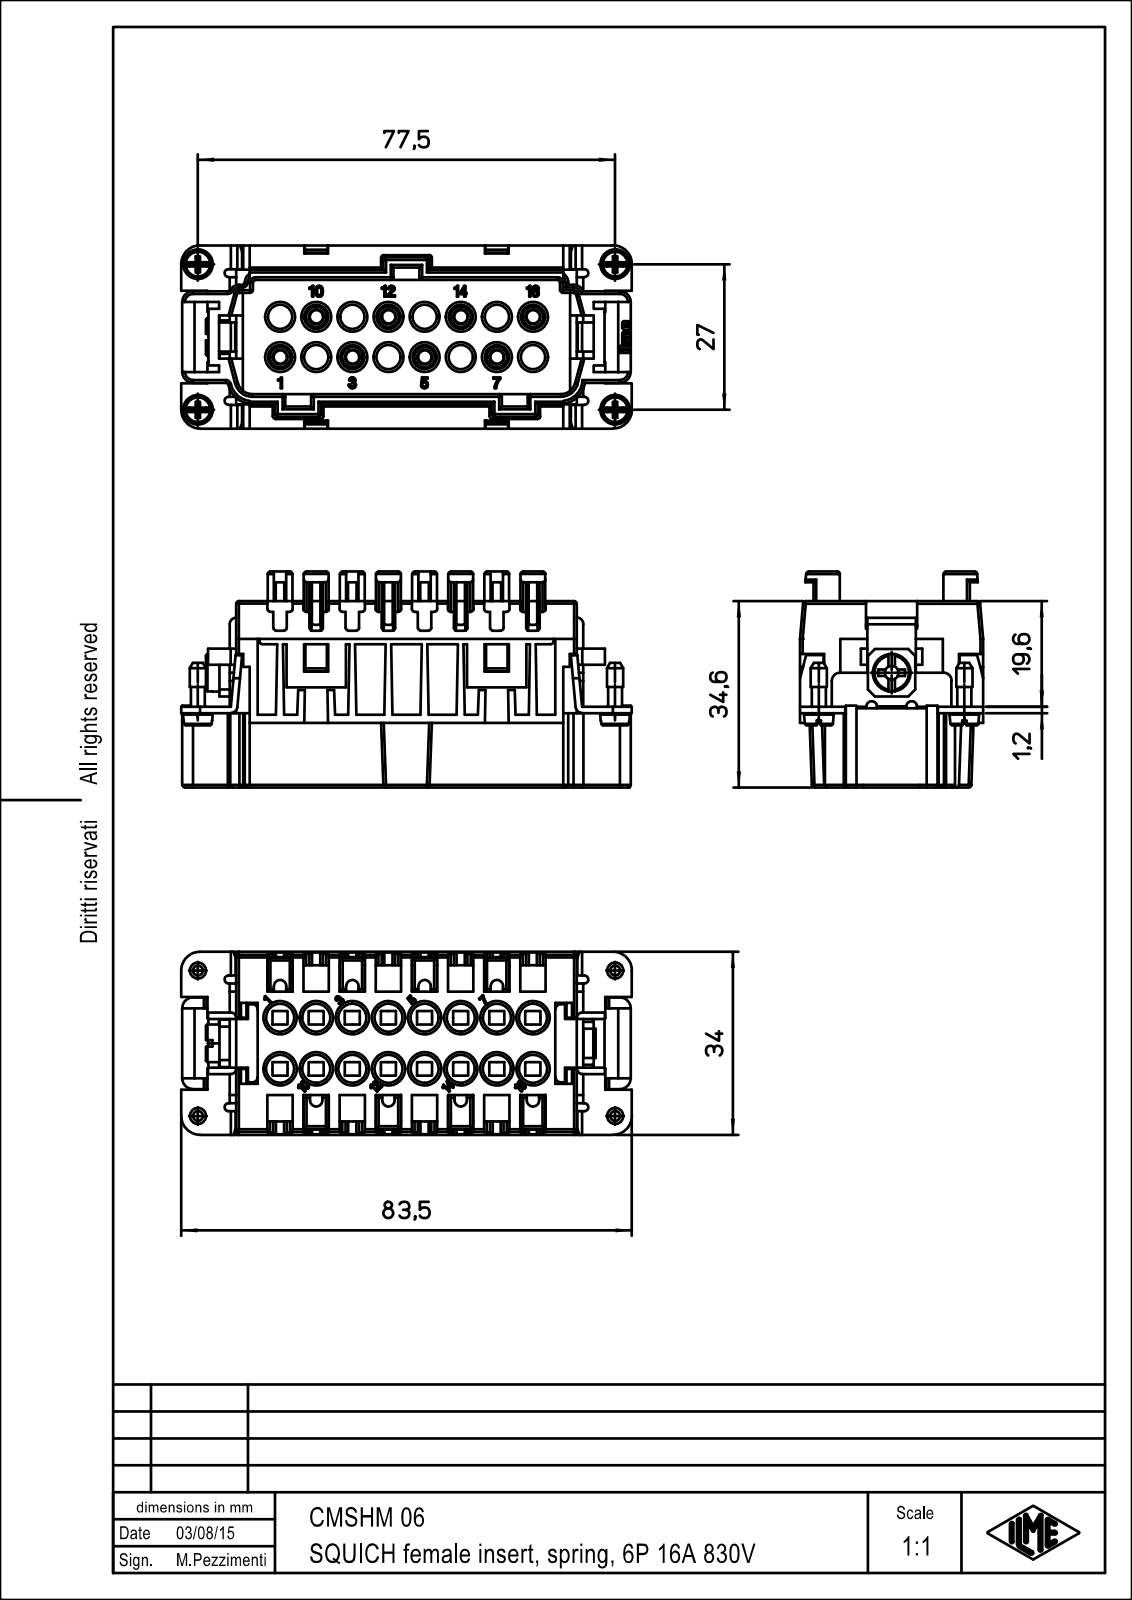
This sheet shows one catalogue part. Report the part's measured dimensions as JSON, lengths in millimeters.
{"part_name": "CMSHM_06", "step_written_by": "Creo Elements/Direct Modeling 18.1F 24-Jul-2014 (C) Parametric Technology GmbH (AUTOMOTIVE_DESIGN)", "units": "millimeters", "bodies": {"solids": 1, "faces": 2212, "planar": 1503, "cylindrical": 464, "other": 245}, "overall_size": [83.6, 40.1, 34], "volume_mm3": 46893, "surface_area_mm2": 28666, "round_holes": [[5.2, 16], [2.48, 8], [2.8, 4], [2.58, 1], [4.2, 1]], "round_bosses_or_shafts": [[2.48, 8], [5.5, 4], [3, 4], [2.6, 4], [7, 1], [6, 1], [4, 1]], "partial_cylinders_radius": [[0.5, 153], [0.3, 19], [1, 12], [2, 10], [1.15, 8], [1.2, 6], [0.29, 5], [0.75, 4]], "face_to_face_distances": [1.5, 4.9, 26.1, 20.1, 27.6, 1.2, 6.4, 4, 12.5, 32.5], "hole_center_spacings": [13.4, 6.7, 11.62, 16.43, 26.8, 20.1, 22.23, 1]}
